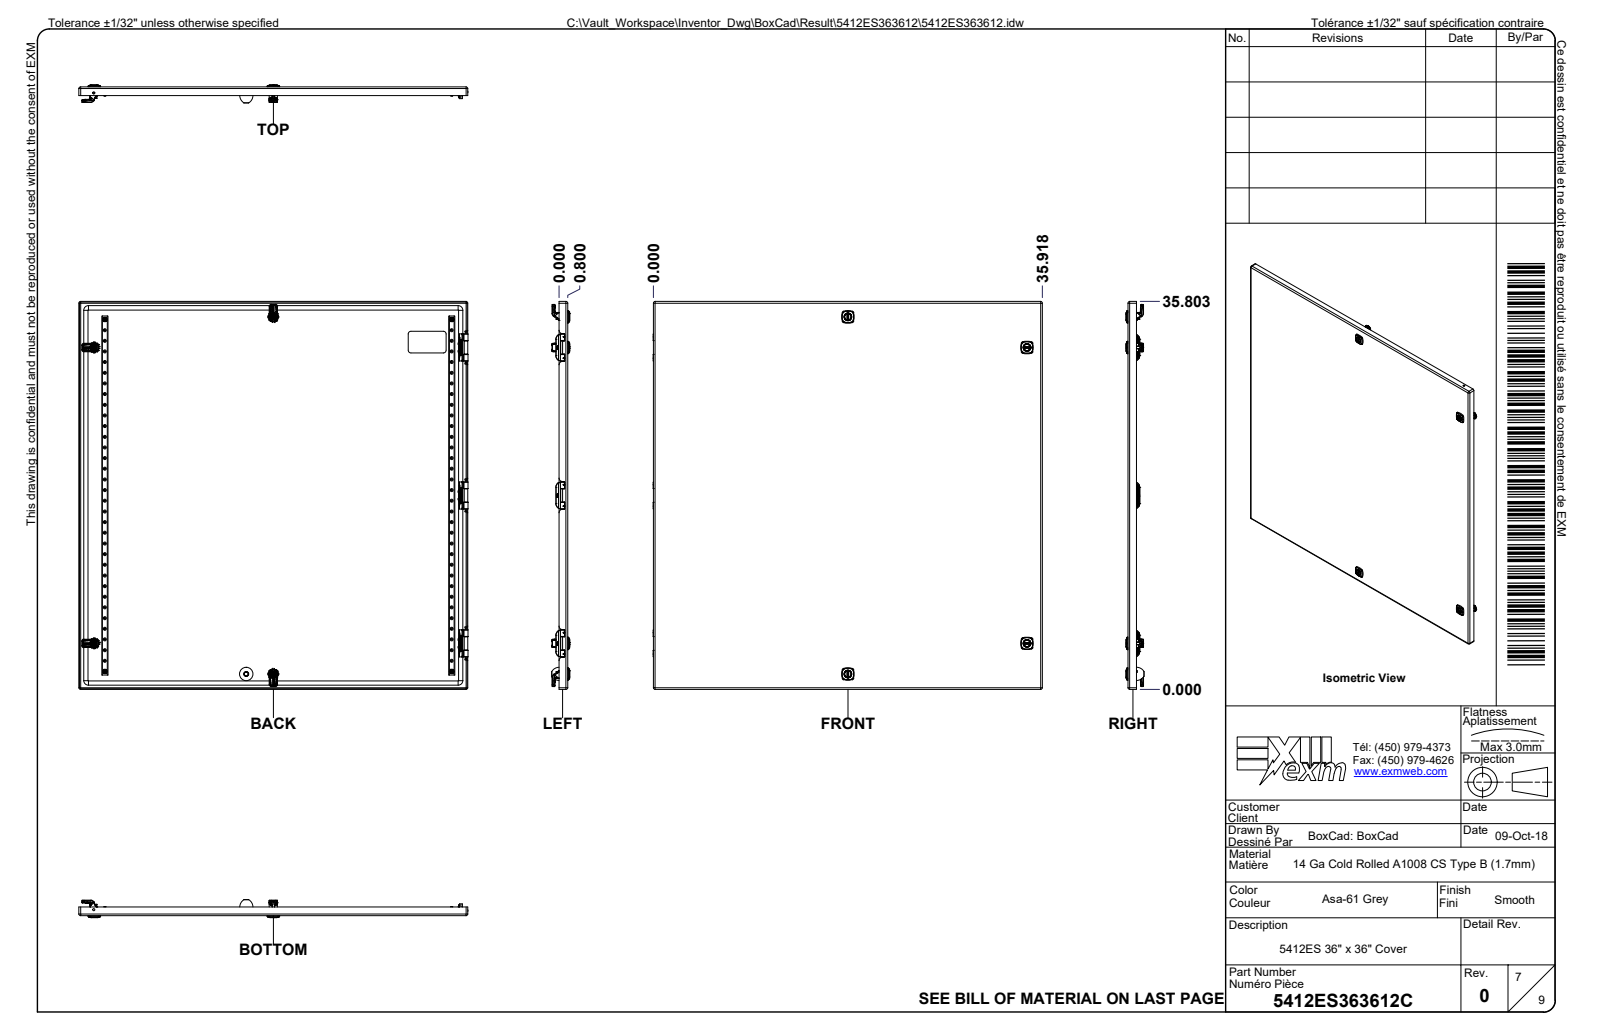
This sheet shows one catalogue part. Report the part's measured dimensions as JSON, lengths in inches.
{"part_name": "5412ES363612; 5412ES363612B; 5412ES363612B-P; STK-Q-16005 (+8 more)", "step_written_by": "Autodesk Inventor 2024 (AUTOMOTIVE_DESIGN)", "units": "inches", "bodies": {"solids": 103, "faces": 17863, "planar": 5759, "cylindrical": 4326, "other": 7778}, "overall_size": [36.018, 36, 13.295], "volume_in3": 466.9, "surface_area_in2": 12329, "round_holes": [[0.165, 64], [0.03, 14], [0.043, 12], [0.315, 12], [0.201, 11], [0.27, 8], [0.311, 8], [0.178, 6], [0.5, 5], [0.197, 4], [0.268, 4], [0.29, 4]], "round_bosses_or_shafts": [[0.237, 64], [0.03, 14], [0.232, 13], [0.039, 12], [0.717, 8], [0.311, 8], [0.262, 8], [0.177, 5]], "partial_cylinders_radius": [[0.02, 439], [0.01, 243], [0.039, 184], [0.008, 156], [0.012, 92], [0.016, 44], [0.016, 36], [0.031, 32]], "face_to_face_distances": [0.068, 13.052, 35.932, 12.983, 13.12, 0.942, 0.874, 12.109, 12.178, 1.047], "hole_center_spacings": [13.652, 1.969, 16.125, 17.287, 33.394, 36.056, 37.569, 0.984]}
